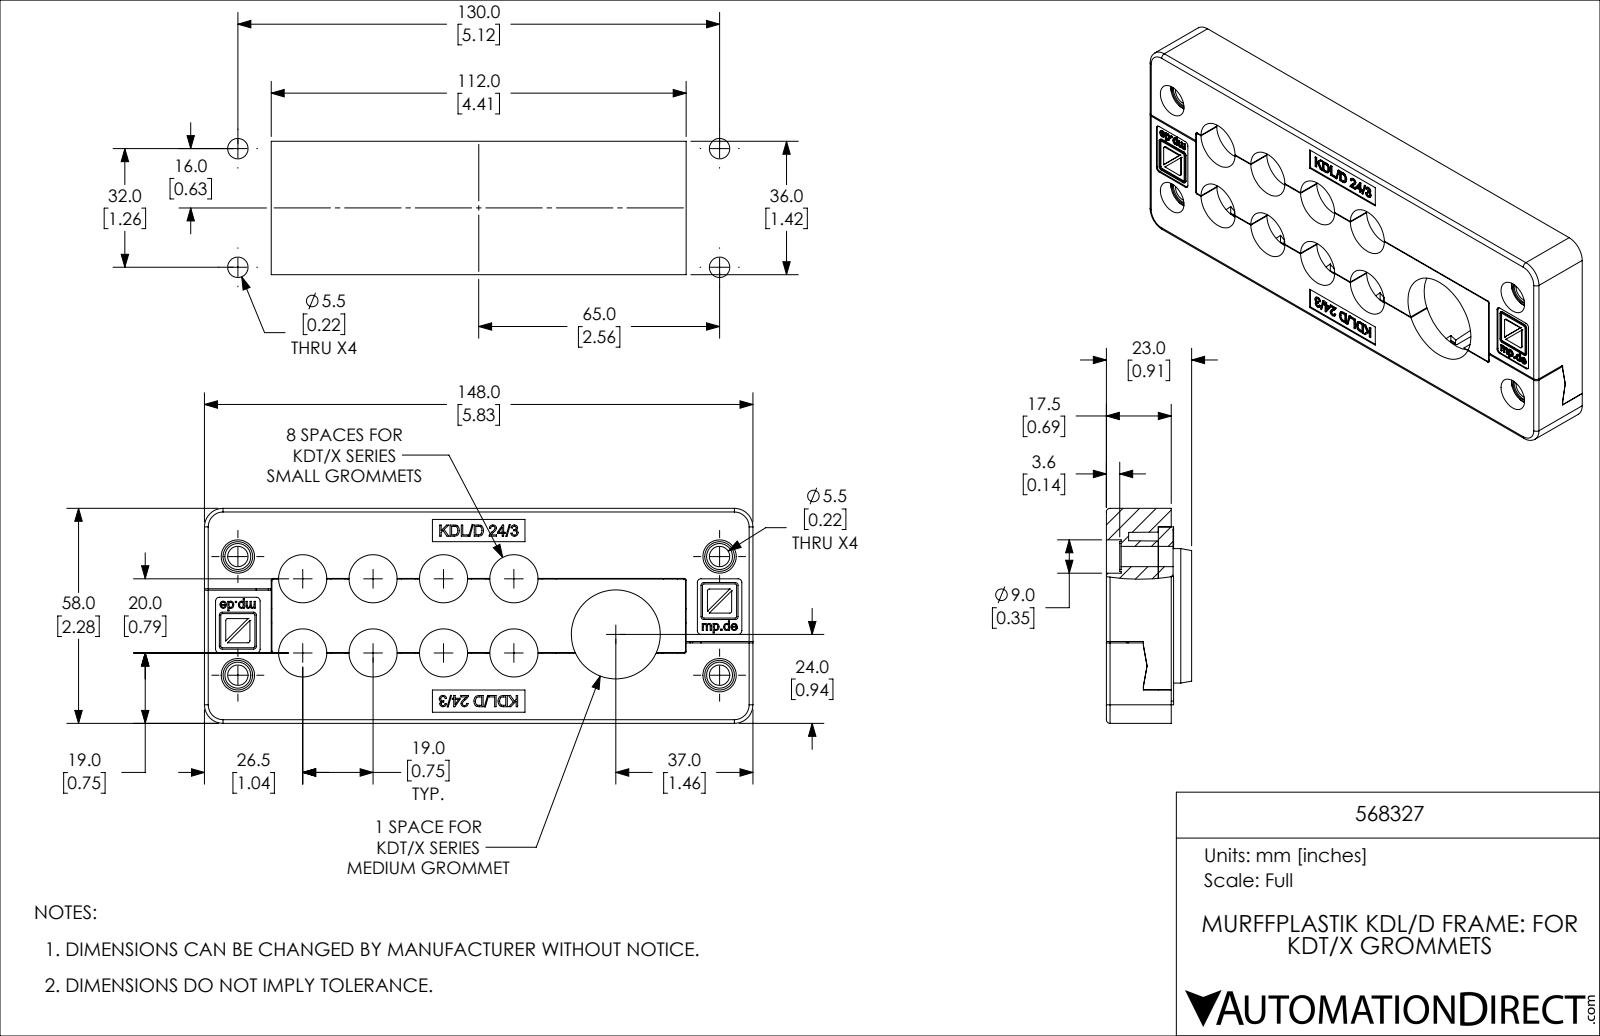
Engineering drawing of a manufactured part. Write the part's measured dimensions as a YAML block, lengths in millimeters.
part_name: "568327"
step_written_by: "SolidWorks 2019 (CONFIG_CONTROL_DESIGN)"
units: millimeters
bodies: {solids: 4, faces: 1597, planar: 939, cylindrical: 274, other: 384}
overall_size: [148, 58, 23]
volume: 112300
surface_area: 60530
round_holes:
  - {diameter: 13, count: 8}
  - {diameter: 15, count: 8}
  - {diameter: 5, count: 6}
  - {diameter: 5.5, count: 4}
  - {diameter: 7, count: 4}
  - {diameter: 9, count: 4}
  - {diameter: 6, count: 2}
  - {diameter: 24, count: 1}
  - {diameter: 24.9, count: 1}
round_bosses_or_shafts:
  - {diameter: 8, count: 4}
partial_cylinders:
  - {radius: 0.5, count: 39}
  - {radius: 1, count: 24}
  - {radius: 0.4, count: 12}
  - {radius: 0.8, count: 8}
  - {radius: 0.1, count: 4}
  - {radius: 0.2, count: 4}
  - {radius: 0.3, count: 4}
  - {radius: 5, count: 4}
face_to_face_distances: [5, 4, 6, 14, 53, 0.5, 3.5, 11.5, 12, 18]
hole_center_spacings: [19, 27.6, 0.5, 18.5, 20, 20, 38, 43]
